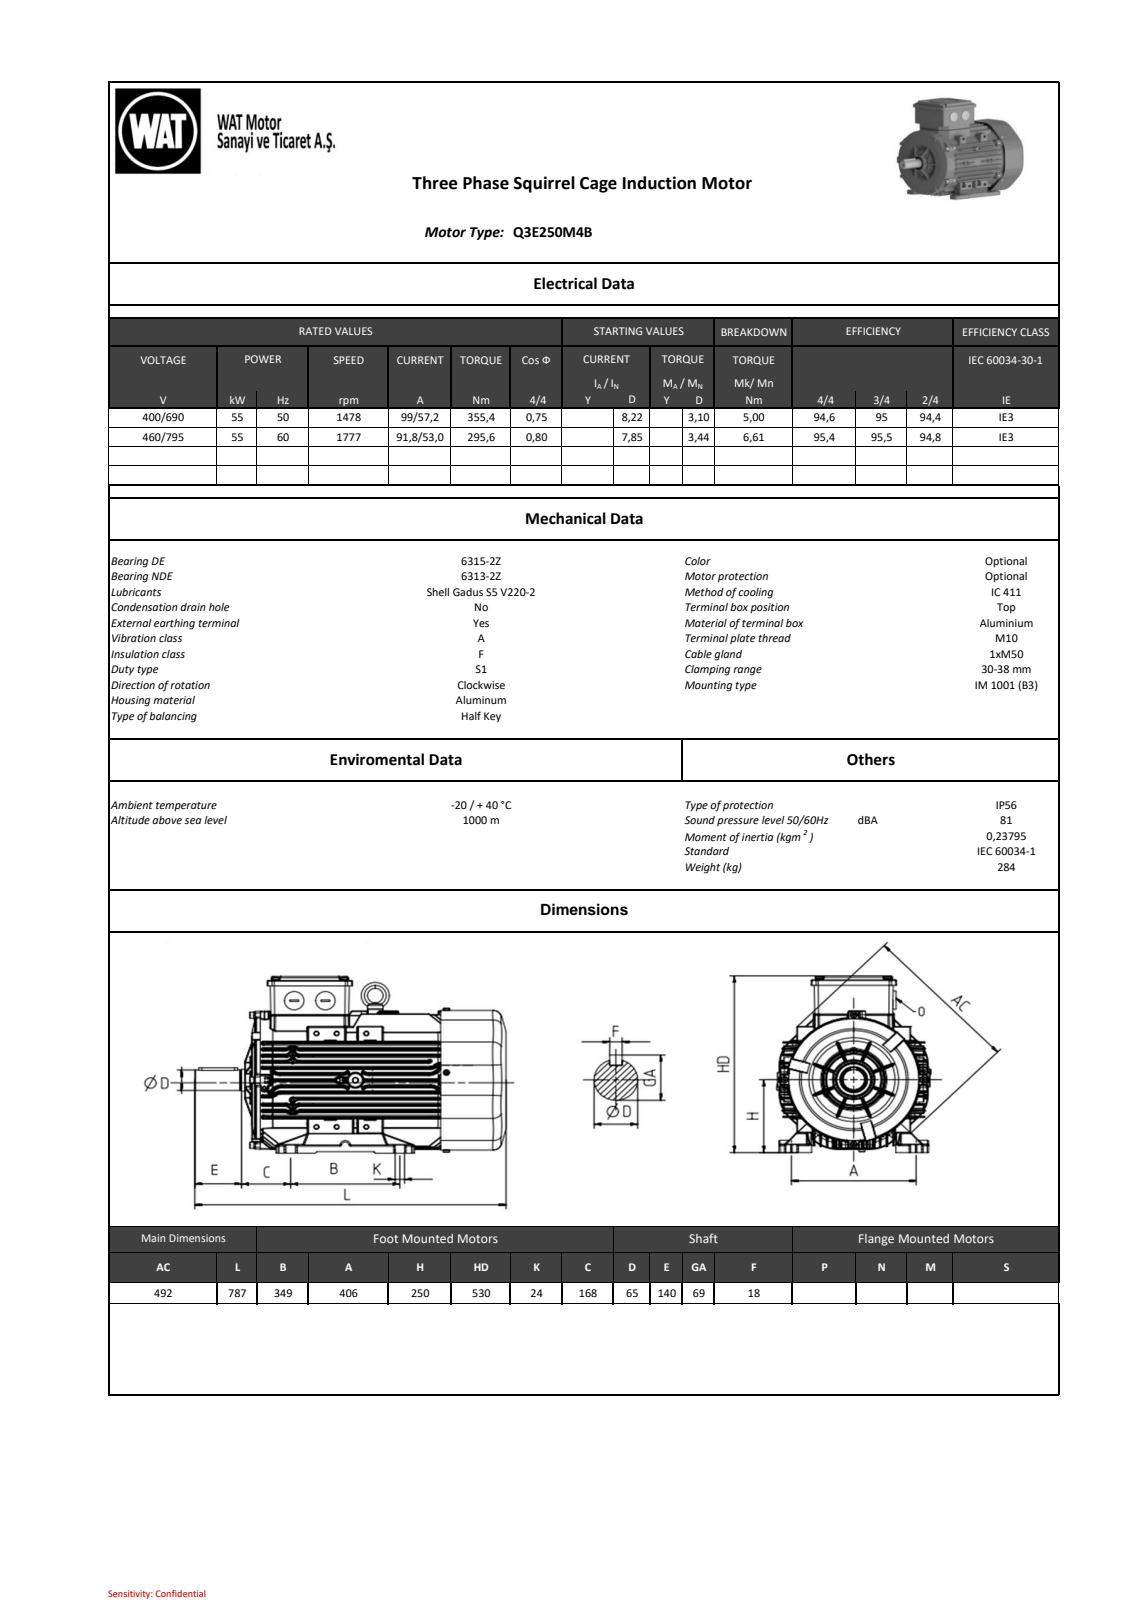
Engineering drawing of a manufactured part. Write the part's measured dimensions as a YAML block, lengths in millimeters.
part_name: "001_objects"
step_written_by: "SIEMENS PLM Software NX2206.8101 (AUTOMOTIVE_DESIGN)"
units: millimeters
bodies: {solids: 0, faces: 15089, planar: 7068, cylindrical: 3870, other: 4151}
overall_size: [787, 532.5, 492]
round_holes:
  - {diameter: 8.5, count: 13}
  - {diameter: 9.15, count: 12}
  - {diameter: 10.2, count: 11}
  - {diameter: 6, count: 8}
  - {diameter: 0.7, count: 6}
  - {diameter: 5, count: 5}
  - {diameter: 7.5, count: 5}
  - {diameter: 11, count: 5}
  - {diameter: 4.3, count: 4}
  - {diameter: 5.5, count: 4}
  - {diameter: 6.5, count: 4}
  - {diameter: 6.86, count: 4}
round_bosses_or_shafts:
  - {diameter: 10, count: 18}
  - {diameter: 15.73, count: 12}
  - {diameter: 18.1, count: 11}
  - {diameter: 8, count: 6}
  - {diameter: 14.8, count: 4}
  - {diameter: 12.73, count: 4}
  - {diameter: 5, count: 4}
  - {diameter: 5.85, count: 3}
partial_cylinders:
  - {radius: 1, count: 966}
  - {radius: 0.2, count: 356}
  - {radius: 2, count: 312}
  - {radius: 0.5, count: 274}
  - {radius: 2.5, count: 151}
  - {radius: 5, count: 117}
  - {radius: 4, count: 105}
  - {radius: 0.3, count: 52}
face_to_face_distances: [8, 189.81, 5, 15.53, 3, 169.04, 20.77, 14.83, 184.57, 5.24]
hole_center_spacings: [7.4, 156, 146.34, 68.18, 98.65, 186.17, 192.6, 220.06]
